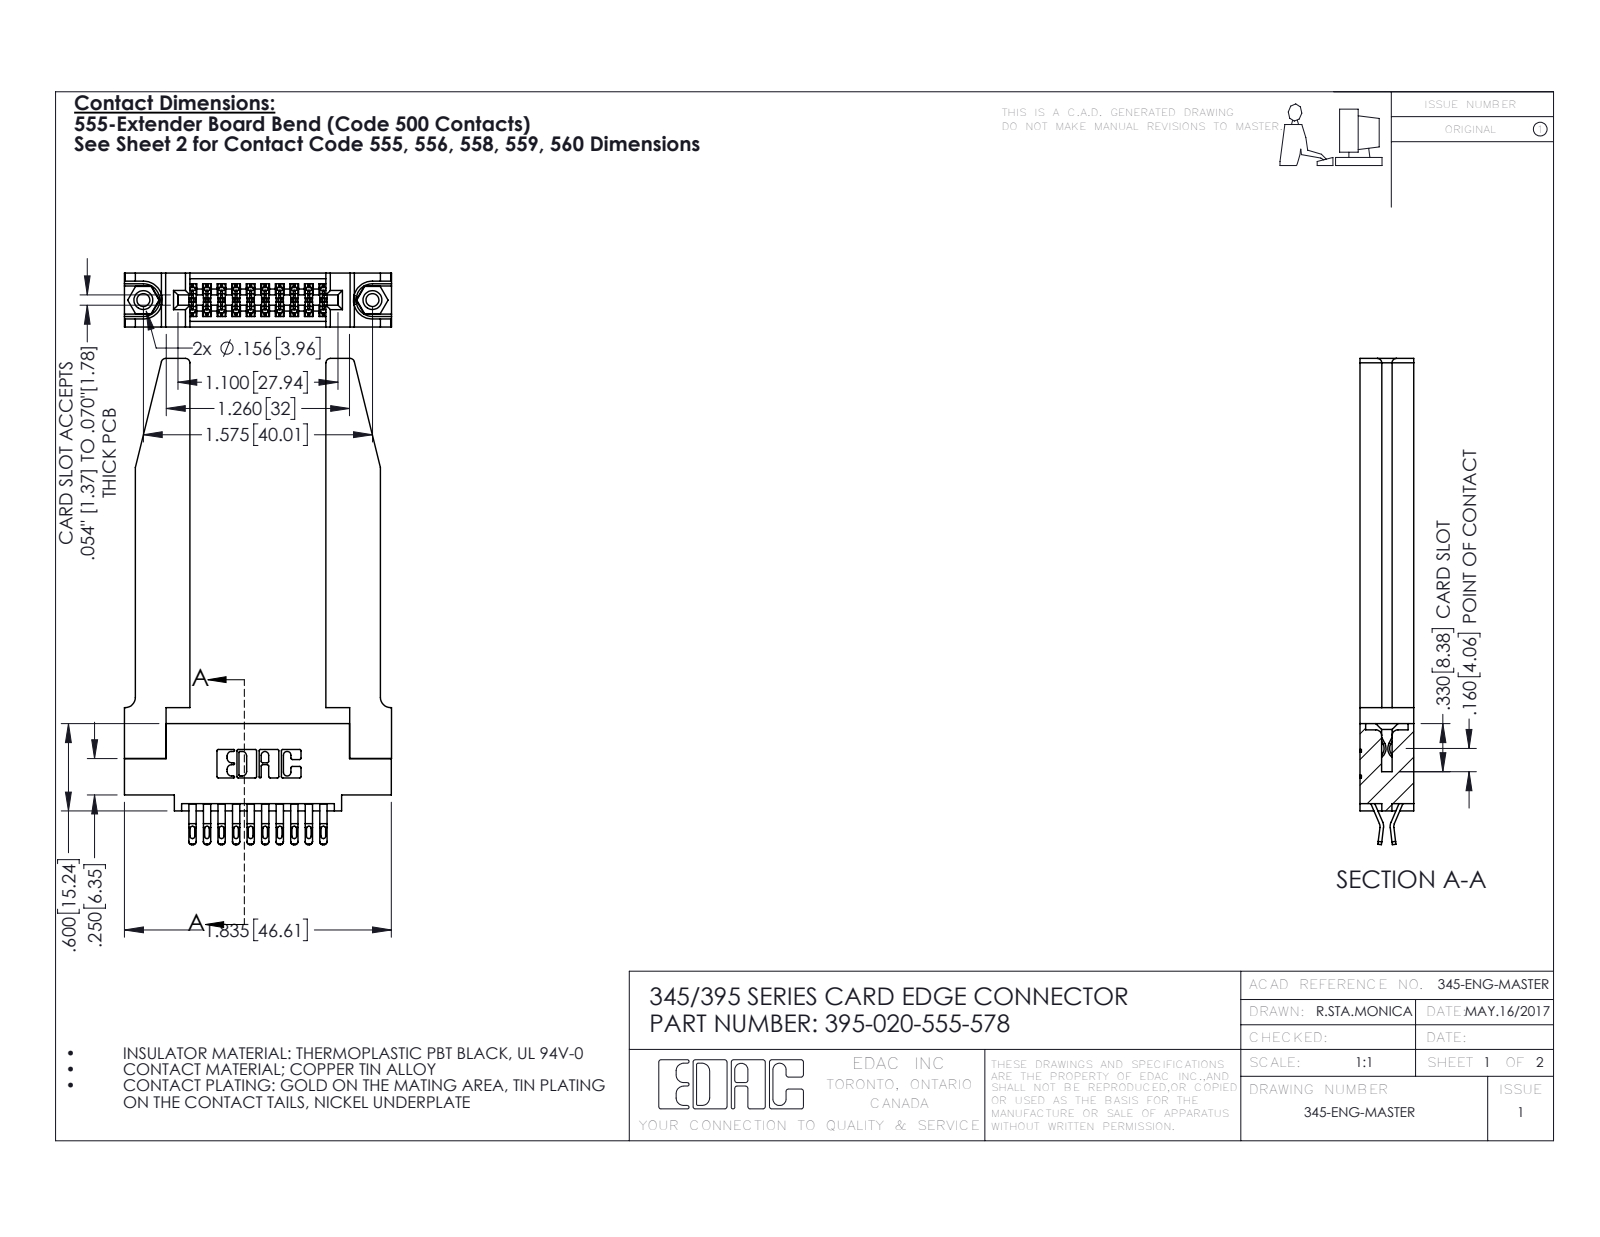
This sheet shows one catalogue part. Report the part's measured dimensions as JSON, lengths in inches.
{"part_name": "345 Part_0.110 Offset - 0.156 Dia-TH; 395-020-555-578; 345-250-001_345-250-001-102; 345-220-078_345-220-078 (+1 more)", "step_written_by": "SolidWorks 2016 (CONFIG_CONTROL_DESIGN)", "units": "inches", "bodies": {"solids": 25, "faces": 1484, "planar": 846, "cylindrical": 586, "other": 52}, "overall_size": [3.342, 1.836, 0.37], "volume_in3": 0.732, "surface_area_in2": 19.76, "round_holes": [[0.089, 2], [0.125, 2], [0.156, 2], [0.064, 1]], "round_bosses_or_shafts": [[0.155, 2]], "partial_cylinders_radius": [[0.016, 50], [0.02, 40], [0.006, 30], [0.01, 22], [0.03, 8], [0.007, 6], [0.031, 6], [0.026, 3]], "face_to_face_distances": [0.37, 0.072, 0.298, 0.148, 0.15, 0.22, 0.077, 0.935, 0.025, 0.2], "hole_center_spacings": [0.27, 1.344, 1.575]}
